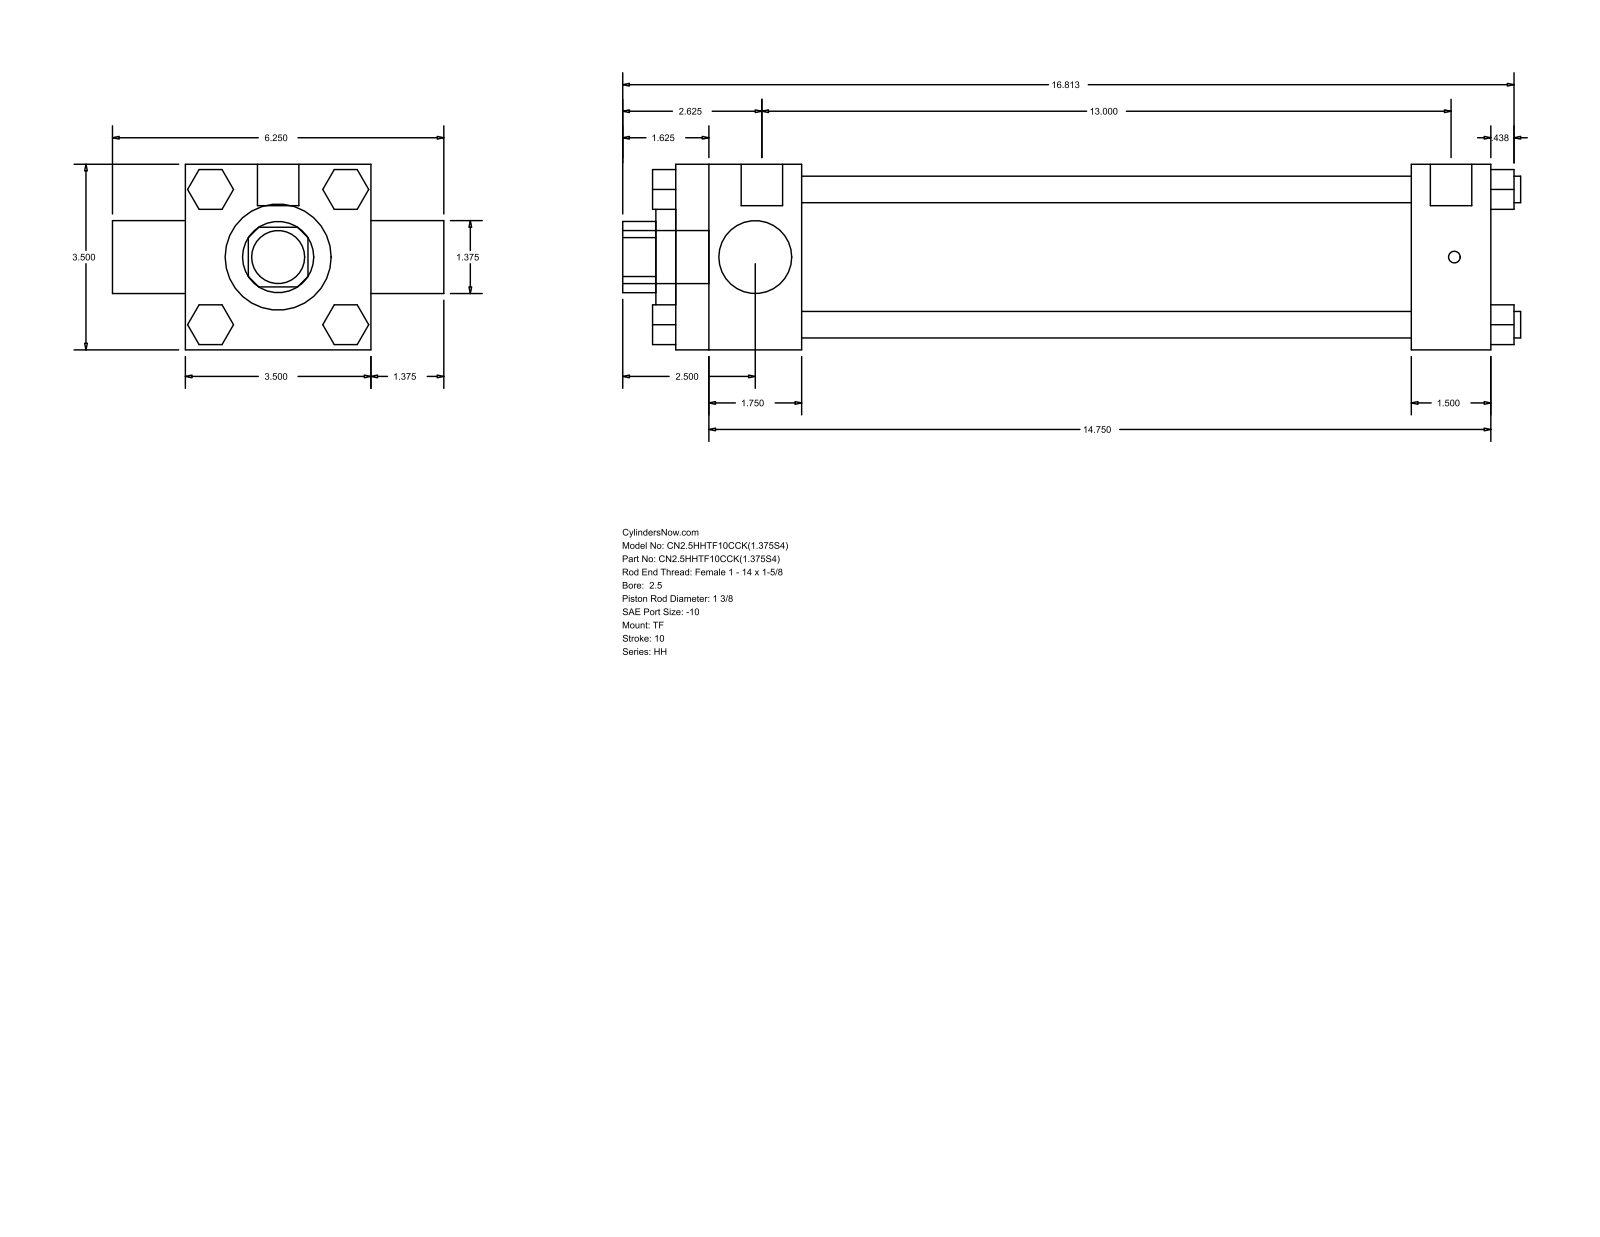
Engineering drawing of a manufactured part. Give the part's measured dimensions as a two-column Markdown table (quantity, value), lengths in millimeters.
| quantity | value |
| --- | --- |
| part name | HH_TF__0250_1.375 |
| STEP written by | GSSL Pune (CONFIG_CONTROL_DESIGN) |
| units | millimeters |
| bodies | 0 solids, 120 faces (92 planar, 28 cylindrical, 0 other) |
| overall size | 430.21 × 158.75 × 88.9 |
| round holes (diameter × count) | 34.92 × 2, 50.8 × 1, 73.03 × 1 |
| round bosses / shafts (diameter × count) | 12.7 × 4, 5.56 × 3, 19.84 × 2, 25.4 × 1 |
| partial cylindrical surfaces (radius × count) | 17.06 × 1 |
| main face-to-face distances | 88.9, 390.53, 60.32, 330.21, 352.42, 292.1, 38.11, 19.05, 32.38, 56.09 |
